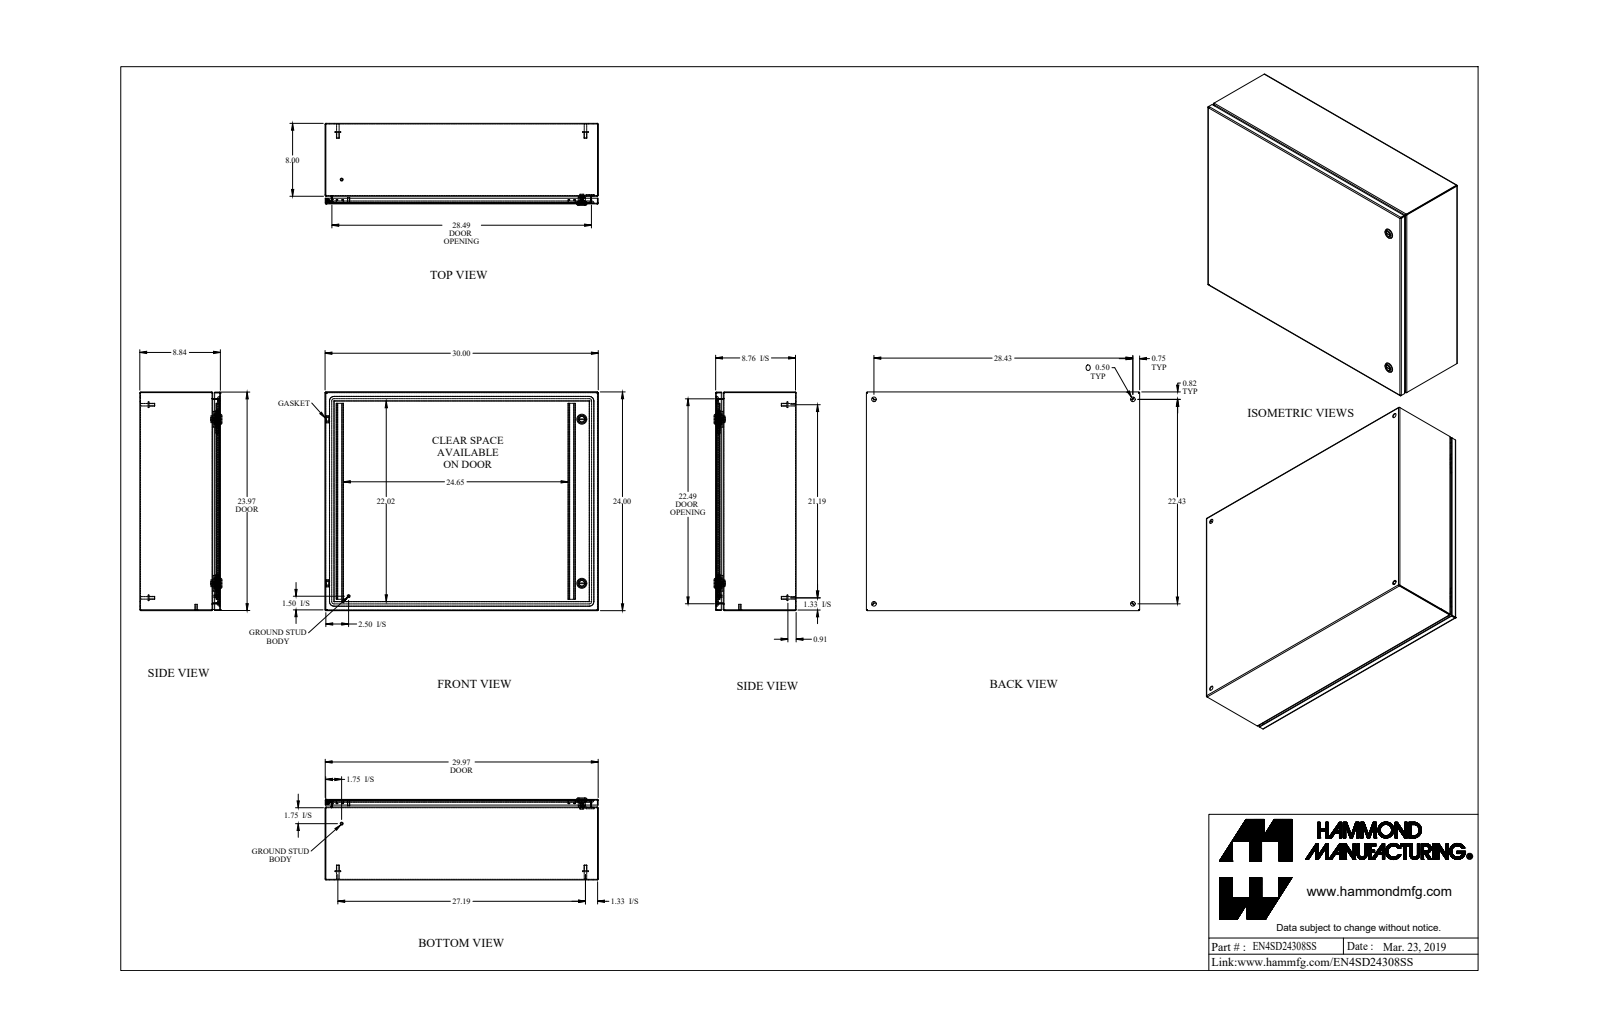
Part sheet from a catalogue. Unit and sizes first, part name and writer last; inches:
Units: inches
Overall size (bounding box): 30 × 24 × 9.002
Round holes (diameter × count): ⌀0.5 ×6, ⌀0.197 ×2, ⌀0.387 ×2, ⌀0.63 ×2, ⌀0.768 ×2, ⌀0.172 ×1, ⌀0.24 ×1, ⌀0.242 ×1
Round bosses / shafts (diameter × count): ⌀0.625 ×6, ⌀0.313 ×6, ⌀0.275 ×4, ⌀1.1 ×2, ⌀0.785 ×2, ⌀0.525 ×2, ⌀0.25 ×2, ⌀0.236 ×2
Partial cylindrical surfaces — rounded edges, fillets, slot ends (radius × count): R0.036 ×20, R0.108 ×20, R0.25 ×16, R0.01 ×12, R0.048 ×12, R0.006 ×4, R0.062 ×4, R0.125 ×4
Main face-to-face distances: 0.072, 8.77, 8.698, 8.842, 23.928, 29.928, 23.856, 24, 29.856, 30
Hole centre spacings: 22.428, 28.428, 36.21, 2.393, 2.458, 17.999, 20.202, 20.273
Volume: 194.3 in³ · Surface area: 5 436 in²
Bodies: 29 solids, 821 faces (414 planar, 263 cylindrical, 144 other)
Part name (STEP PRODUCT): EN4SD24308SS_Default
STEP written by: SolidWorks 2019 (CONFIG_CONTROL_DESIGN)
